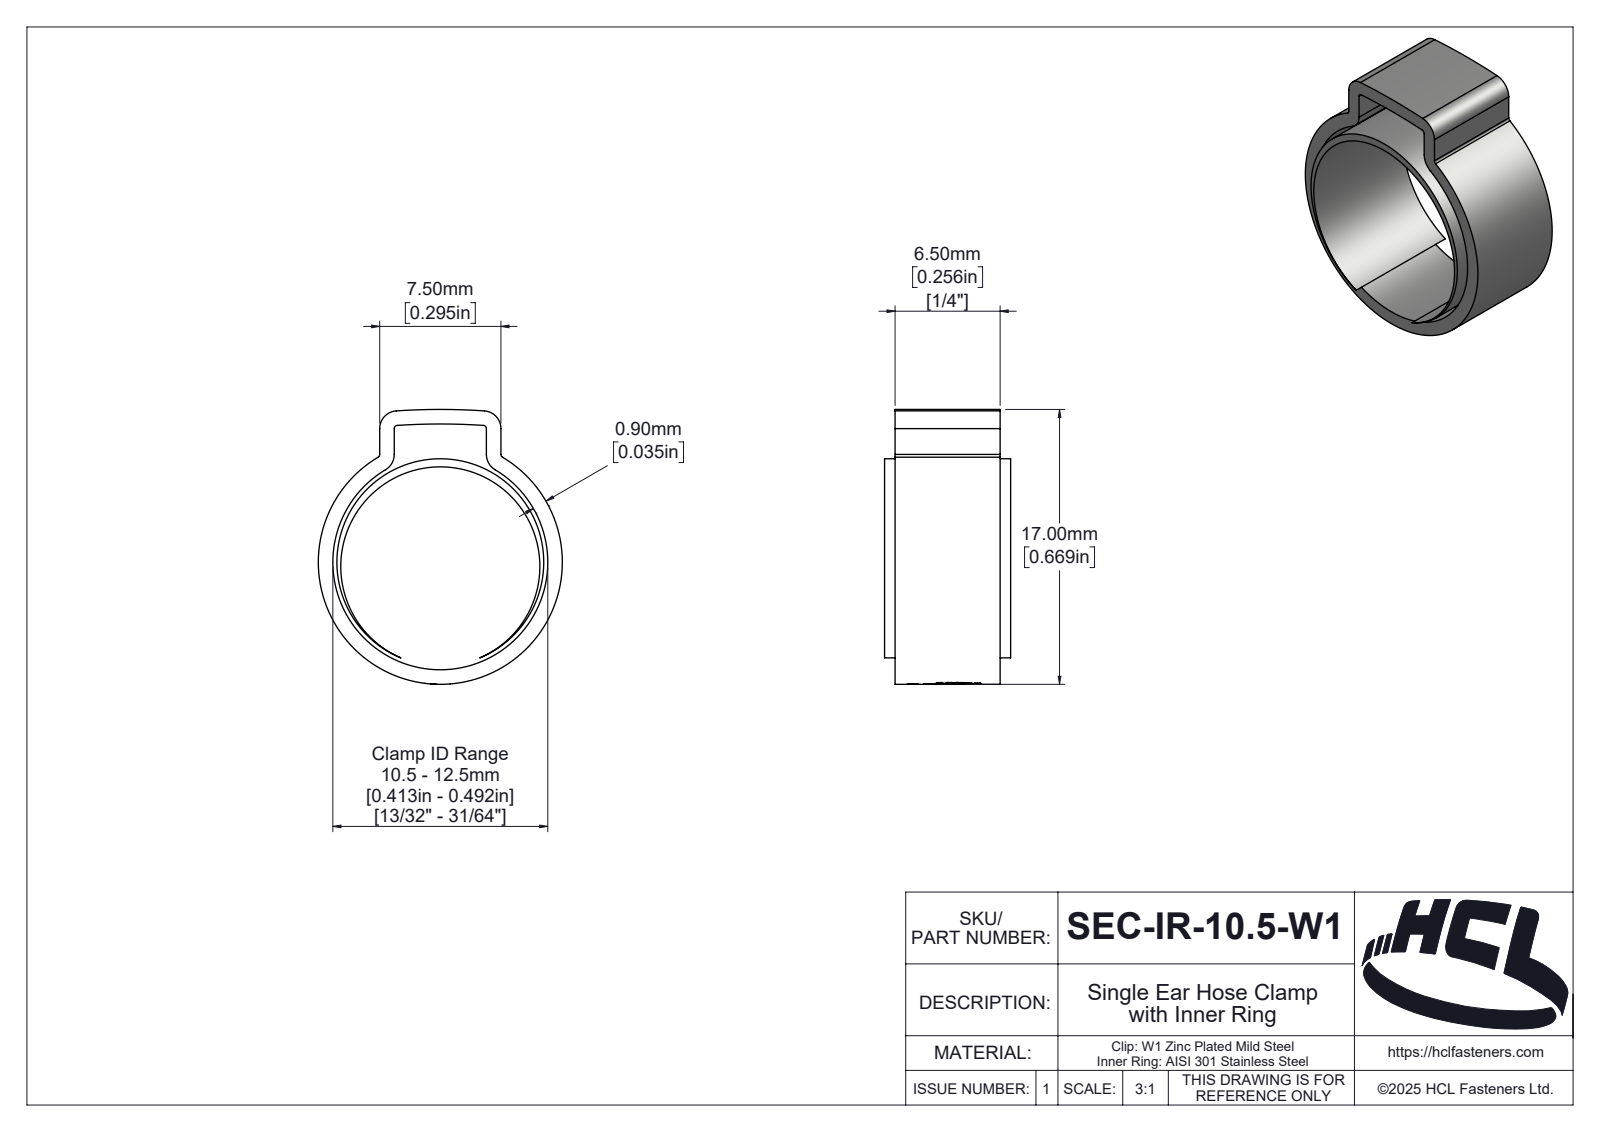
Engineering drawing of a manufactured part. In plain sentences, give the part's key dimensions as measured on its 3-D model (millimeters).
The part is named "SEC-IR-10.5-W1". Its 3-D file was written by "SolidWorks 2025 (AUTOMOTIVE_DESIGN)". It is 2 solids with 131 faces: 10 planar, 72 cylindrical and 49 other. Overall it measures 17 by 15.1 by 7.8 millimeters. Its volume is 360 cubic millimeters and its surface area 1 284 square millimeters. Round holes: 1 of diameter 12.32, 1 of diameter 13.3. Round bosses or shafts: 1 of diameter 15.1, 1 of diameter 12.8. Partial cylindrical surfaces (rounded edges, fillets, slot ends): 4 of radius 0.2, 4 of radius 1.1, 1 of radius 0.2, 1 of radius 0.81, 1 of radius 1.01, 1 of radius 1.06, 1 of radius 1.28, 1 of radius 1.81. The main face-to-face distances are 6.5, 0.9, 6.6, 0.65, 7.15, 7.5, 5.7, 7.8, 3.48, 2.58.
